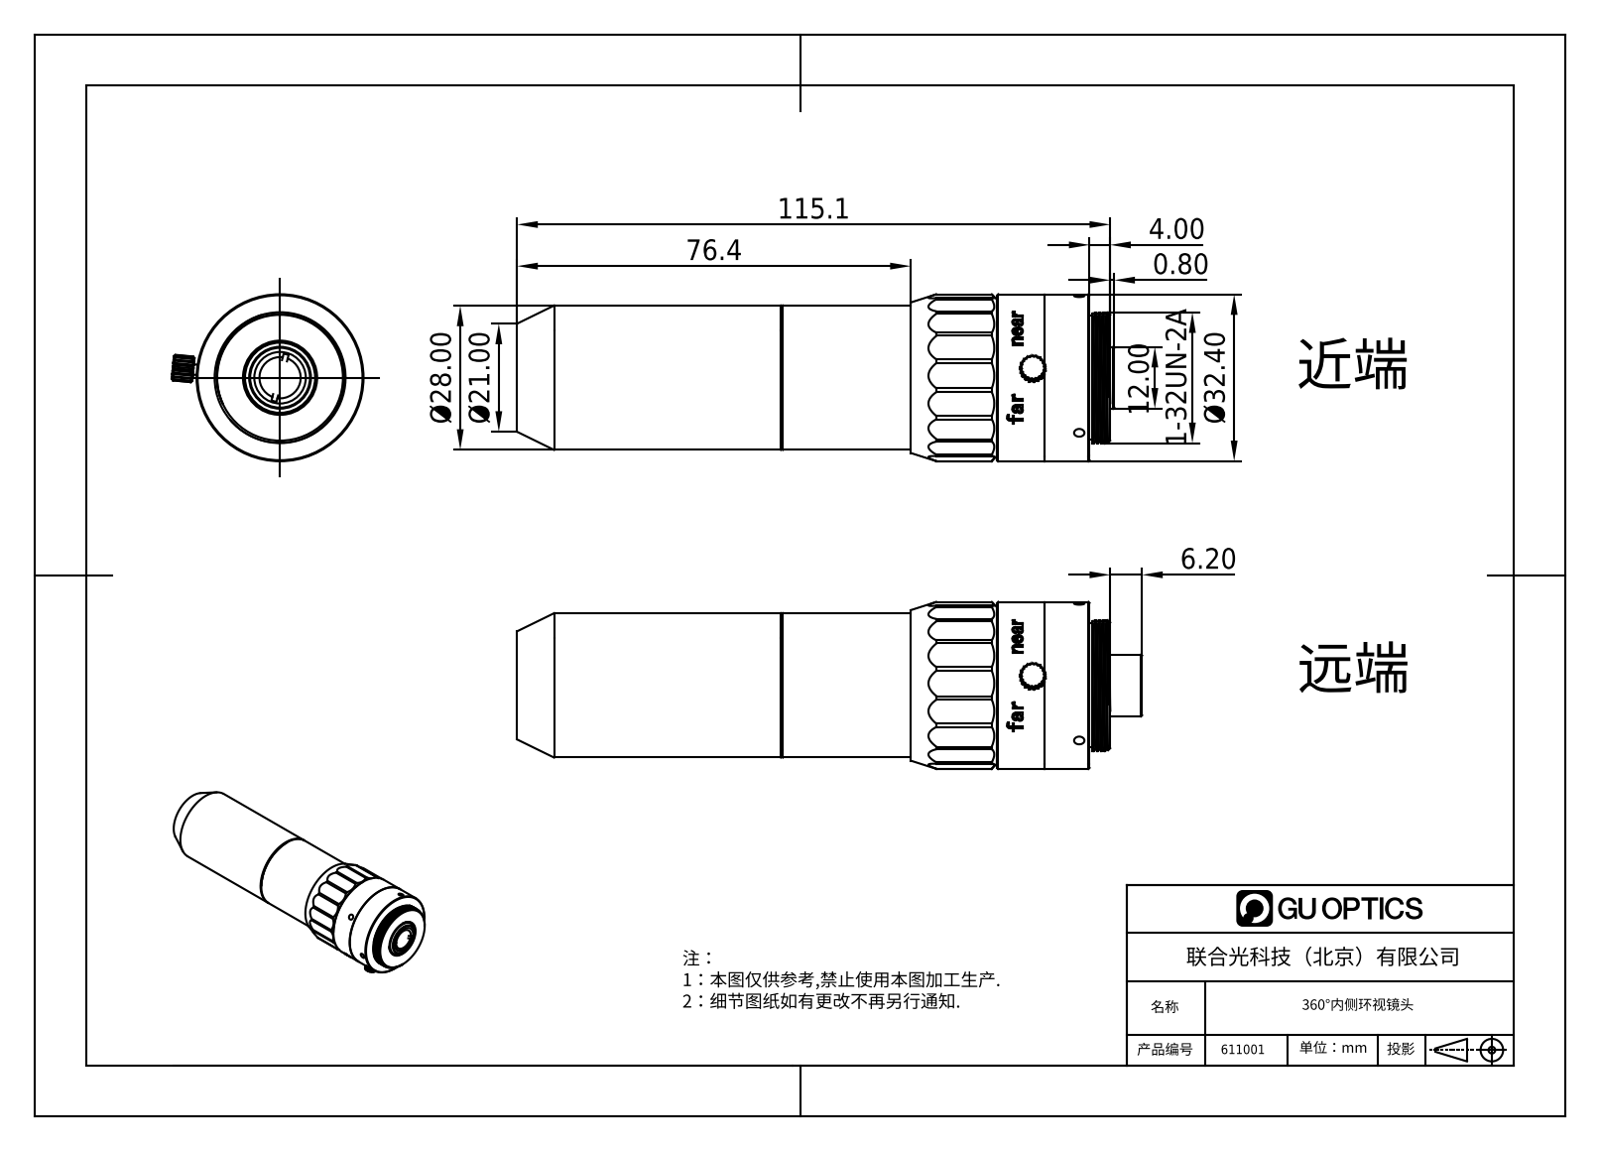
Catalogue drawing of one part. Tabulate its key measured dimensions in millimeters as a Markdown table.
| quantity | value |
| --- | --- |
| part name | 611001 |
| STEP written by | SolidWorks 2020 (CONFIG_CONTROL_DESIGN) |
| units | millimeters |
| bodies | 20 solids, 541 faces (215 planar, 157 cylindrical, 169 other) |
| overall size | 115.92 × 37.21 × 32.4 |
| volume | 104 628 mm³ |
| surface area | 39 630 mm² |
| round holes (diameter × count) | 2 × 6, 3.2 × 3, 0.8 × 2, 0.7 × 1, 3.6 × 1, 5.6 × 1, 6 × 1, 8 × 1, 8.1 × 1, 9 × 1, 9.4 × 1, 9.6 × 1 |
| round bosses / shafts (diameter × count) | 2 × 7, 2.8 × 3, 32.4 × 1, 28 × 1, 26.6 × 1, 25.4 × 1, 24 × 1, 23.2 × 1 |
| partial cylindrical surfaces (radius × count) | 10 × 18, 2.5 × 1, 16.1 × 1 |
| main face-to-face distances | 65.6, 4, 51.7, 13.9, 8, 13.8, 11.8, 25.6, 40, 51.8 |
| hole center spacings | 4.1, 4, 4.01, 8.01 |
